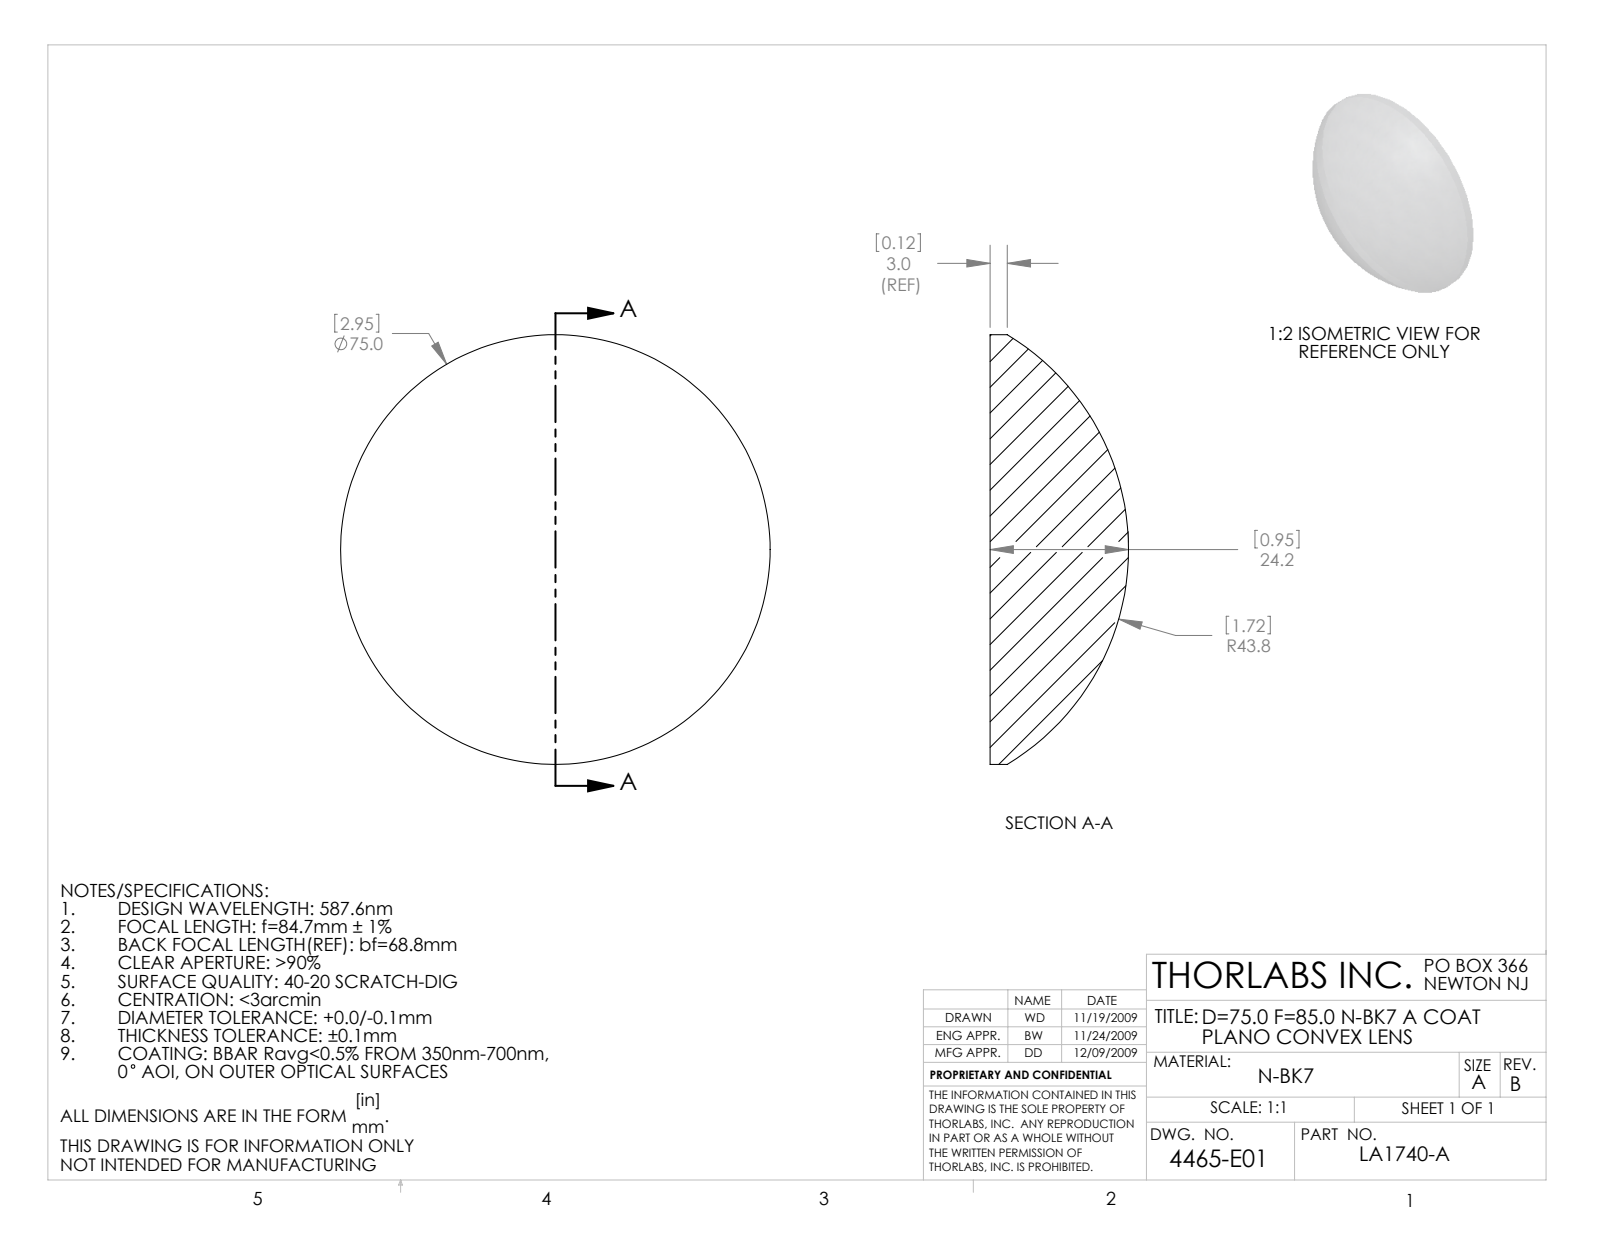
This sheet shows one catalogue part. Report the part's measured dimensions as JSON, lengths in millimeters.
{"part_name": "4465-E0W", "step_written_by": "SolidWorks 2009 (AUTOMOTIVE_DESIGN)", "units": "millimeters", "bodies": {"solids": 1, "faces": 5, "planar": 1, "cylindrical": 2, "other": 2}, "overall_size": [75, 75, 24.18], "volume_mm3": 65003, "surface_area_mm2": 10951, "round_bosses_or_shafts": [[75, 1]]}
